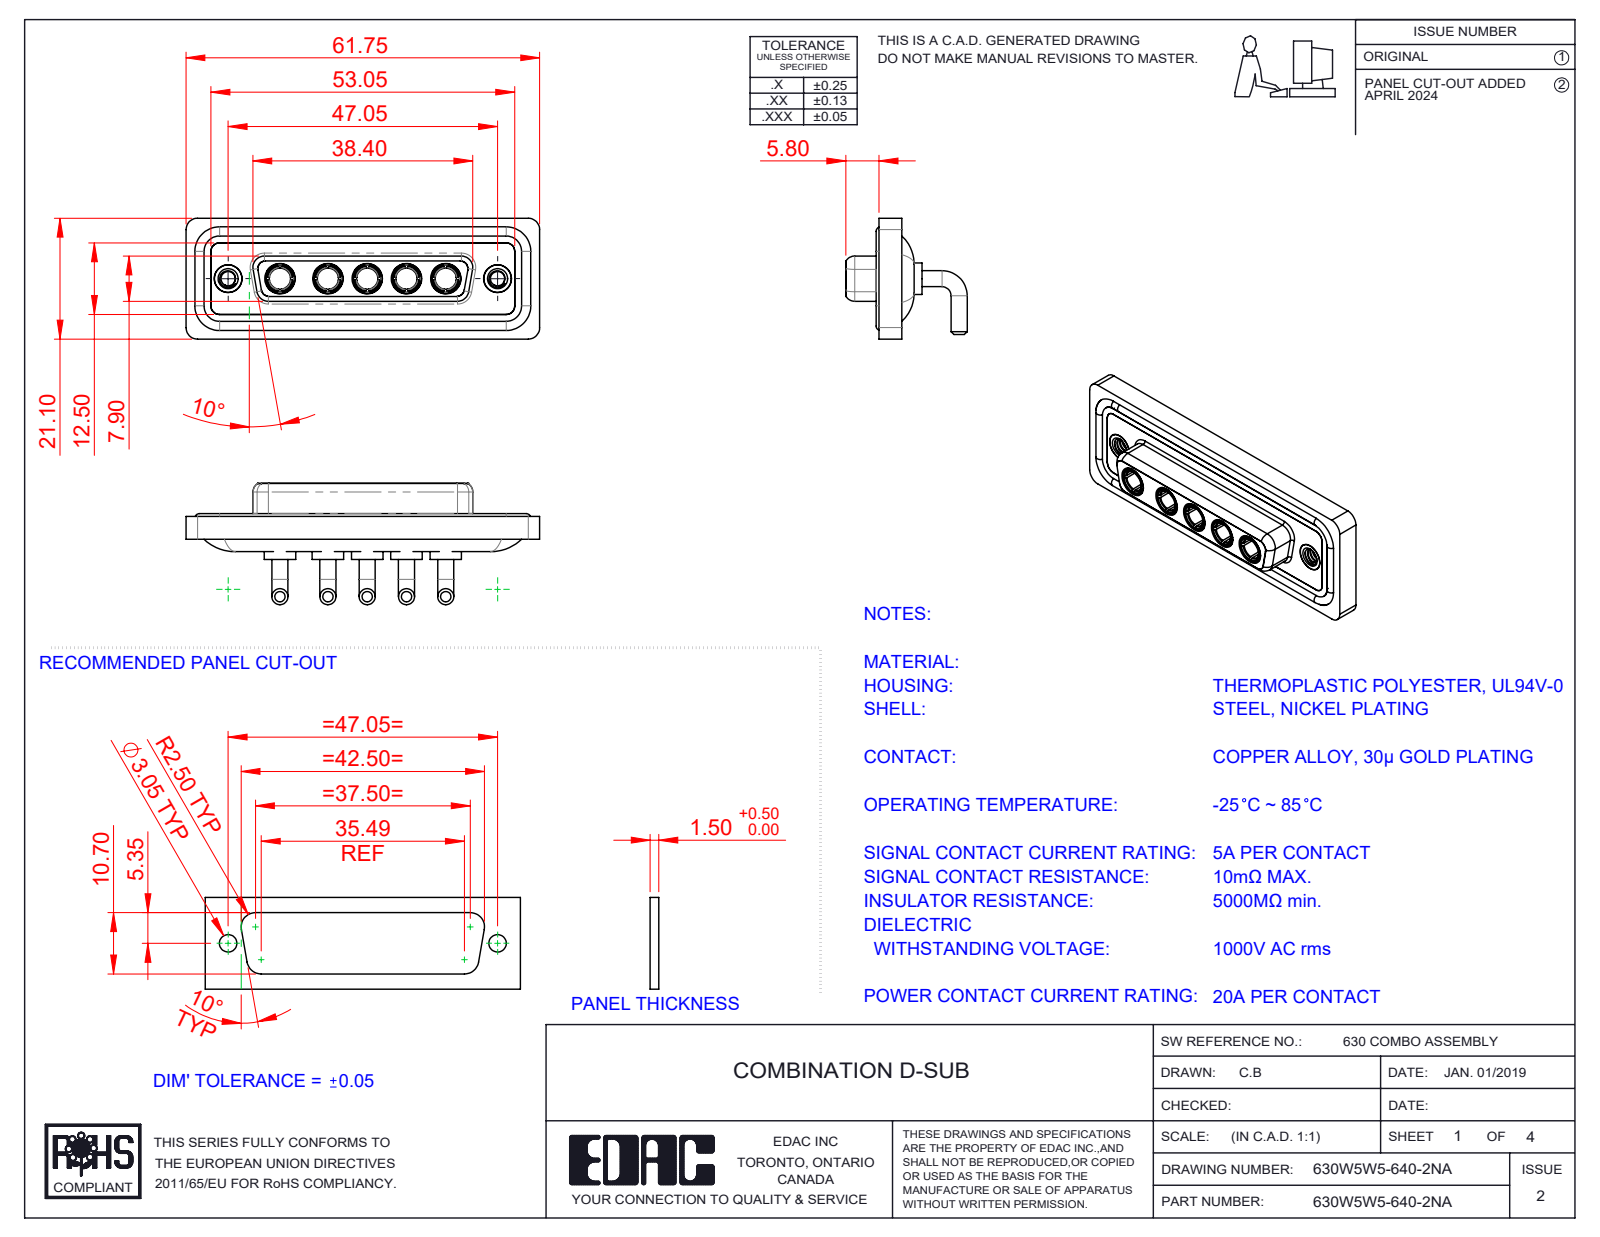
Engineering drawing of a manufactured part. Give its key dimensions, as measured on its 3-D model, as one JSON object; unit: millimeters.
{"part_name": "630W5W5-640-2NA; 630Combo Threaded Rivet_A; 630Combo Shell Front_25 Contacts; 630Combo Waterproof Housing_25 Contacts (+3 more)", "step_written_by": "SolidWorks 2023 (CONFIG_CONTROL_DESIGN)", "units": "millimeters", "bodies": {"solids": 17, "faces": 770, "planar": 250, "cylindrical": 311, "other": 209}, "overall_size": [61.75, 21.2, 21.1], "volume_mm3": 8428, "surface_area_mm2": 13816, "round_holes": [[4.85, 7], [3.7, 5], [5.3, 5], [2.5, 2], [4, 2], [4.05, 2], [5, 2]], "round_bosses_or_shafts": [[2.8, 10], [5.5, 5], [5.2, 5], [4.96, 5], [4.75, 5], [3.75, 5], [1.6, 4], [4.95, 2]], "partial_cylinders_radius": [[1.5, 18], [2, 18], [1.35, 8], [1.6, 8], [2.1, 5], [0.25, 4], [0.5, 4], [0.6, 4]], "face_to_face_distances": [0.4, 1.8, 4.1, 1.1, 1.5, 2.5, 3.1, 3.7, 1.6, 2.9], "hole_center_spacings": [6.86, 9.04, 38.01, 6.87, 8.38, 13.72, 13.73, 15.25]}
